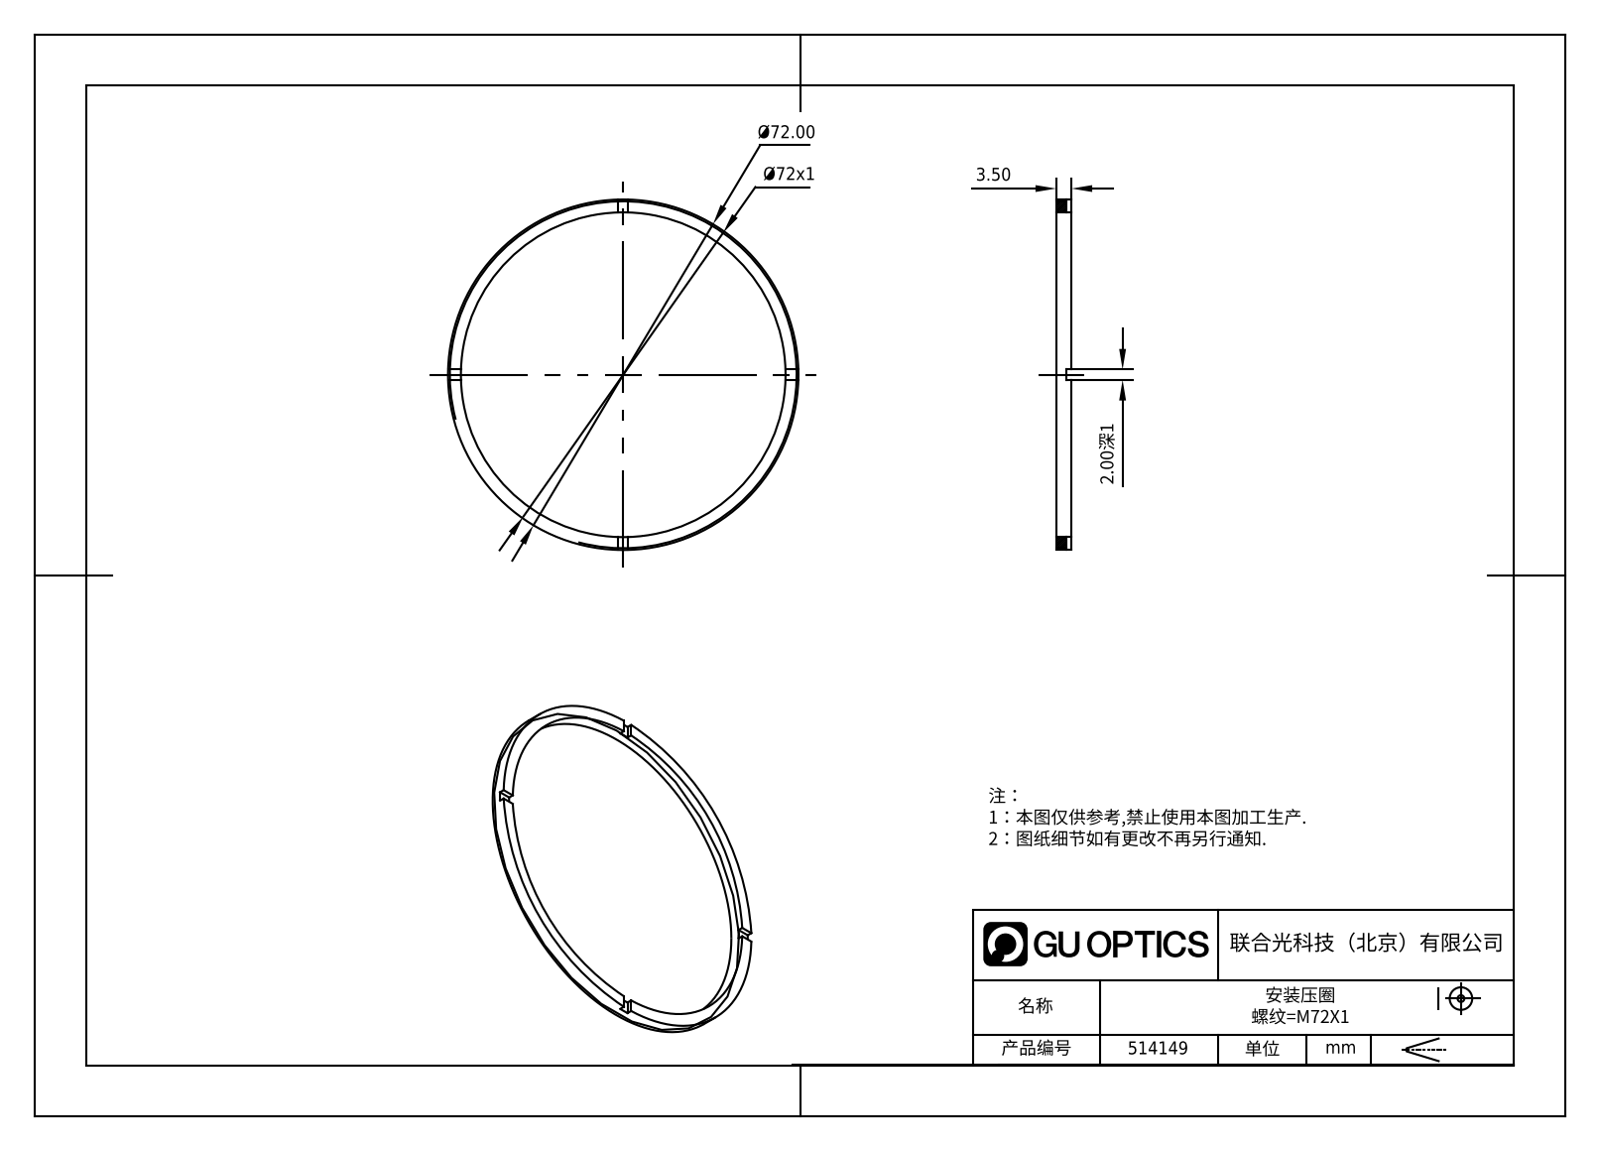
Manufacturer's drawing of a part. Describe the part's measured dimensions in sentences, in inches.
The part is named "514149". Its 3-D file was written by "SolidWorks 2020 (CONFIG_CONTROL_DESIGN)". It is 1 solid with 21 faces: 17 planar, 4 cylindrical and 0 other. Overall it measures 2.835 by 2.835 by 0.138 inches. Its volume is 0.137 cubic inches and its surface area 4.38 square inches. Round holes: 1 of diameter 2.598. Round bosses or shafts: 1 of diameter 2.835. The main face-to-face distances are 0.138, 0.098, 0.039, 0.079.
